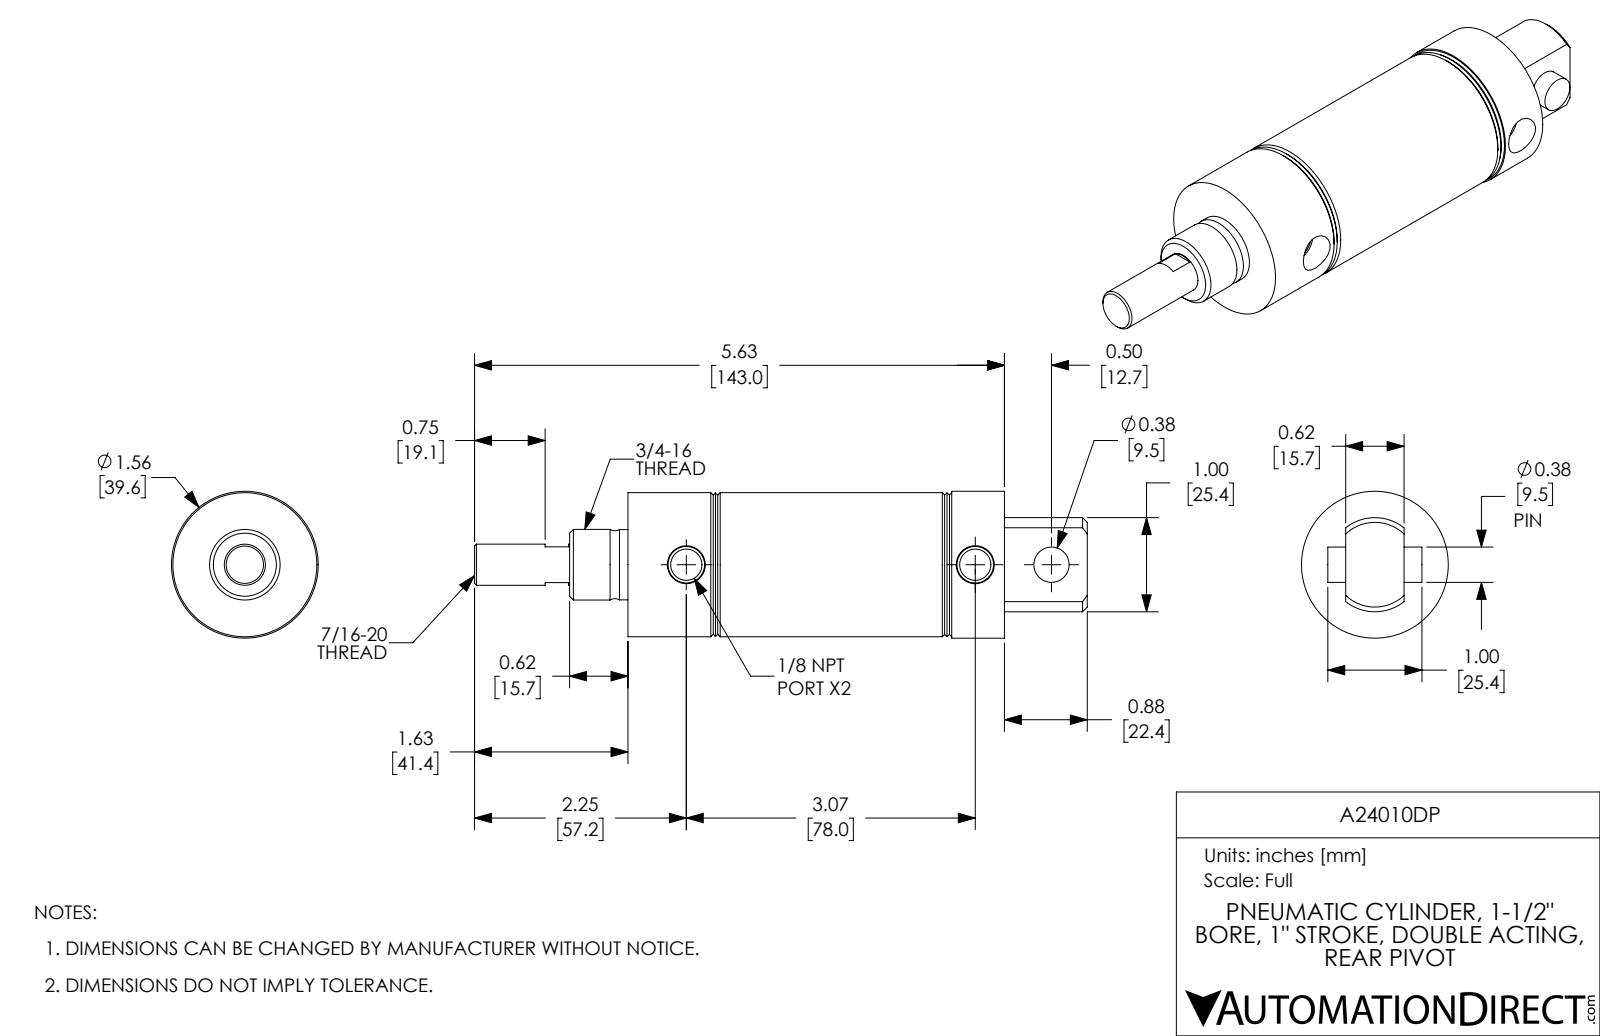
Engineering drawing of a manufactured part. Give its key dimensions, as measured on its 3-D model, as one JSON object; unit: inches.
{"part_name": "A24010DP-MainBody; A24010DP-Rod; A24010DP-Pin; A24010DP", "step_written_by": "SolidWorks 2017 (AUTOMOTIVE_DESIGN)", "units": "inches", "bodies": {"solids": 3, "faces": 84, "planar": 22, "cylindrical": 28, "other": 34}, "overall_size": [6.51, 1.56, 1.56], "volume_in3": 6.63, "surface_area_in2": 54.38, "round_holes": [[0.332, 2], [0.375, 1], [0.437, 1], [1.5, 1]], "round_bosses_or_shafts": [[1.56, 1], [1.53, 1], [0.75, 1], [0.746, 1]], "partial_cylinders_radius": [[0.5, 1]], "face_to_face_distances": [1.25, 2.75, 1, 0.5, 1.5, 2.25, 1.75, 4, 0.62, 0.88], "hole_center_spacings": [0.81, 3.07, 3.88]}
